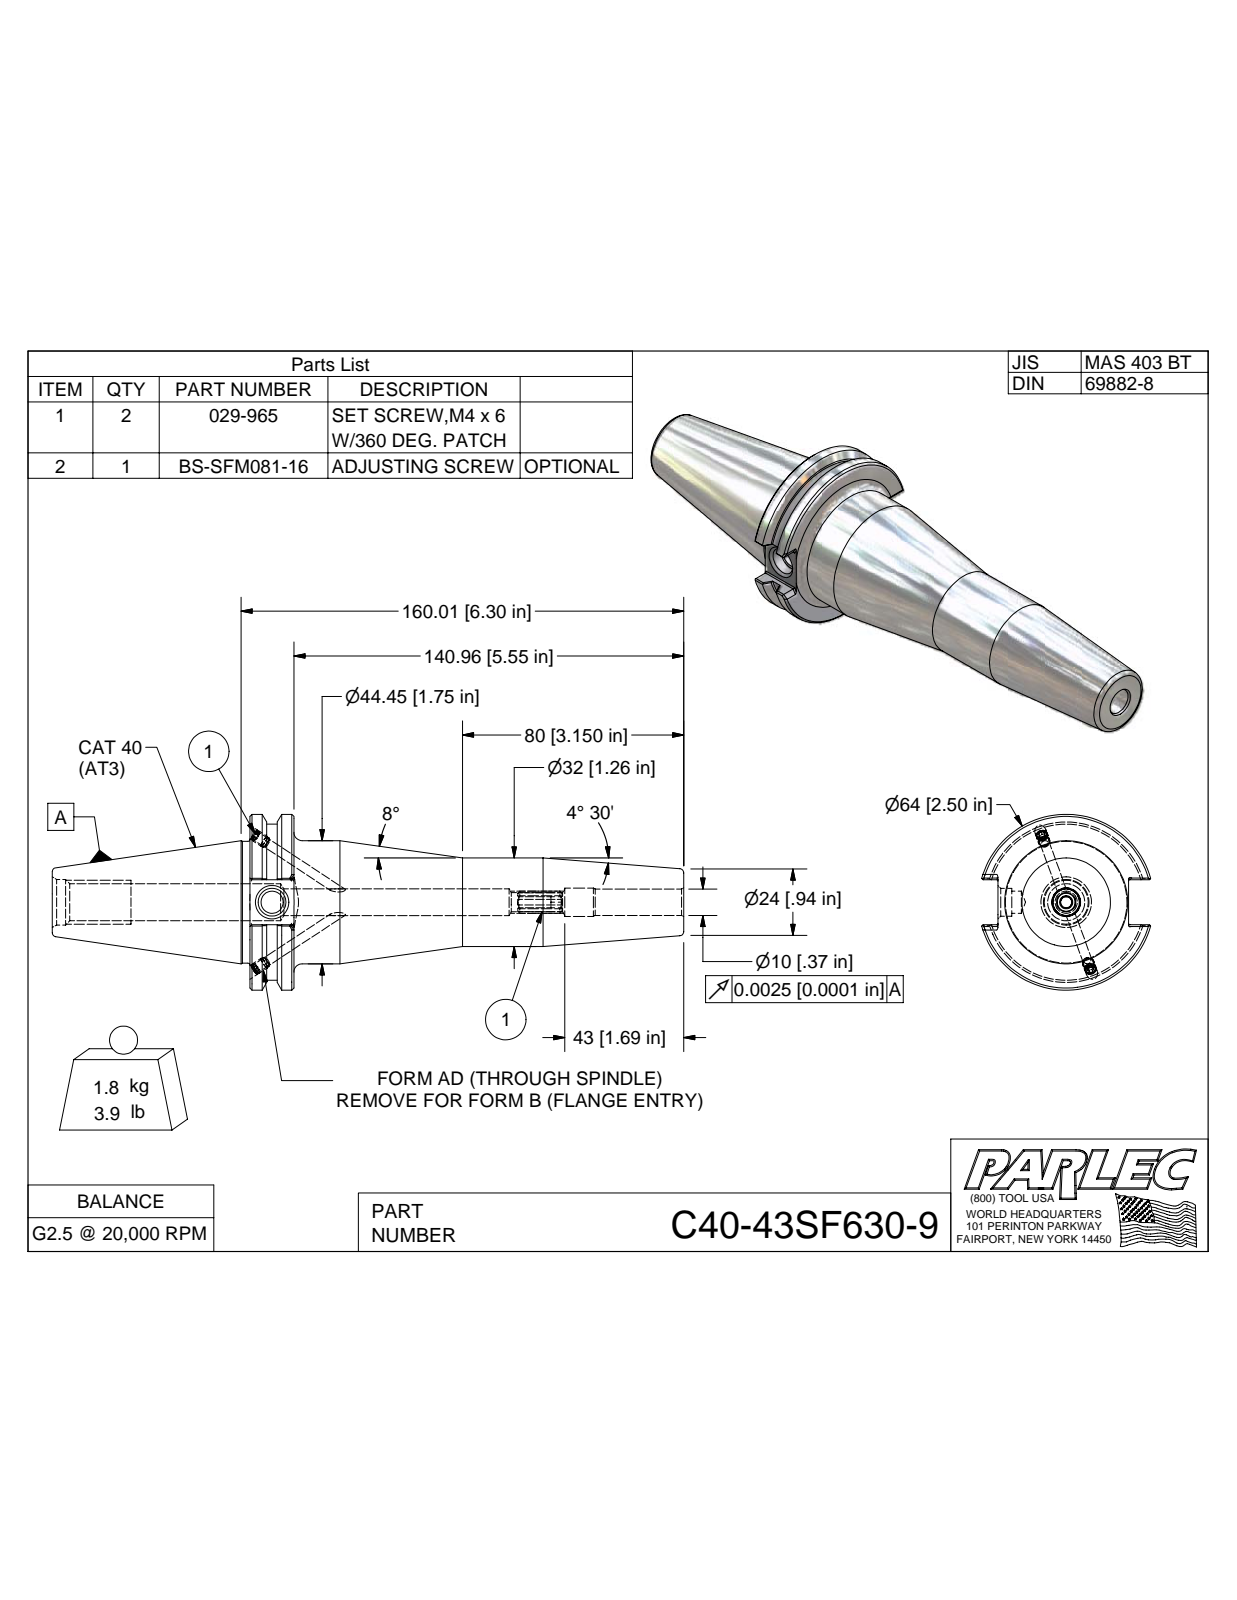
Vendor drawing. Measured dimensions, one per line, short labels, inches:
name: C40-43SF630-9; C40BC-43SF630-9-1; 029-965; BS-SFM081-16
written by: Autodesk Inventor 2009 (AUTOMOTIVE_DESIGN)
unit: in
bodies: 4 solids, 155 faces (66 planar, 35 cylindrical, 54 other)
size: 8.987 × 2.5 × 2.406
volume: 13.63 in³; area: 61.73 in²
holes: 2× ⌀0.13, 2× ⌀0.161, 1× ⌀0.374, 1× ⌀0.404
bosses: 2× ⌀0.165, 2× ⌀0.157, 1× ⌀2.5, 1× ⌀2.219, 1× ⌀1.75, 1× ⌀1.73, 1× ⌀1.26
rounds: 12× R0.02, 1× R0.157
face distances: 0.625, 6.175, 5.55, 0.64, 1.86, 2.812, 3.437, 8.987, 3.201, 0.389
